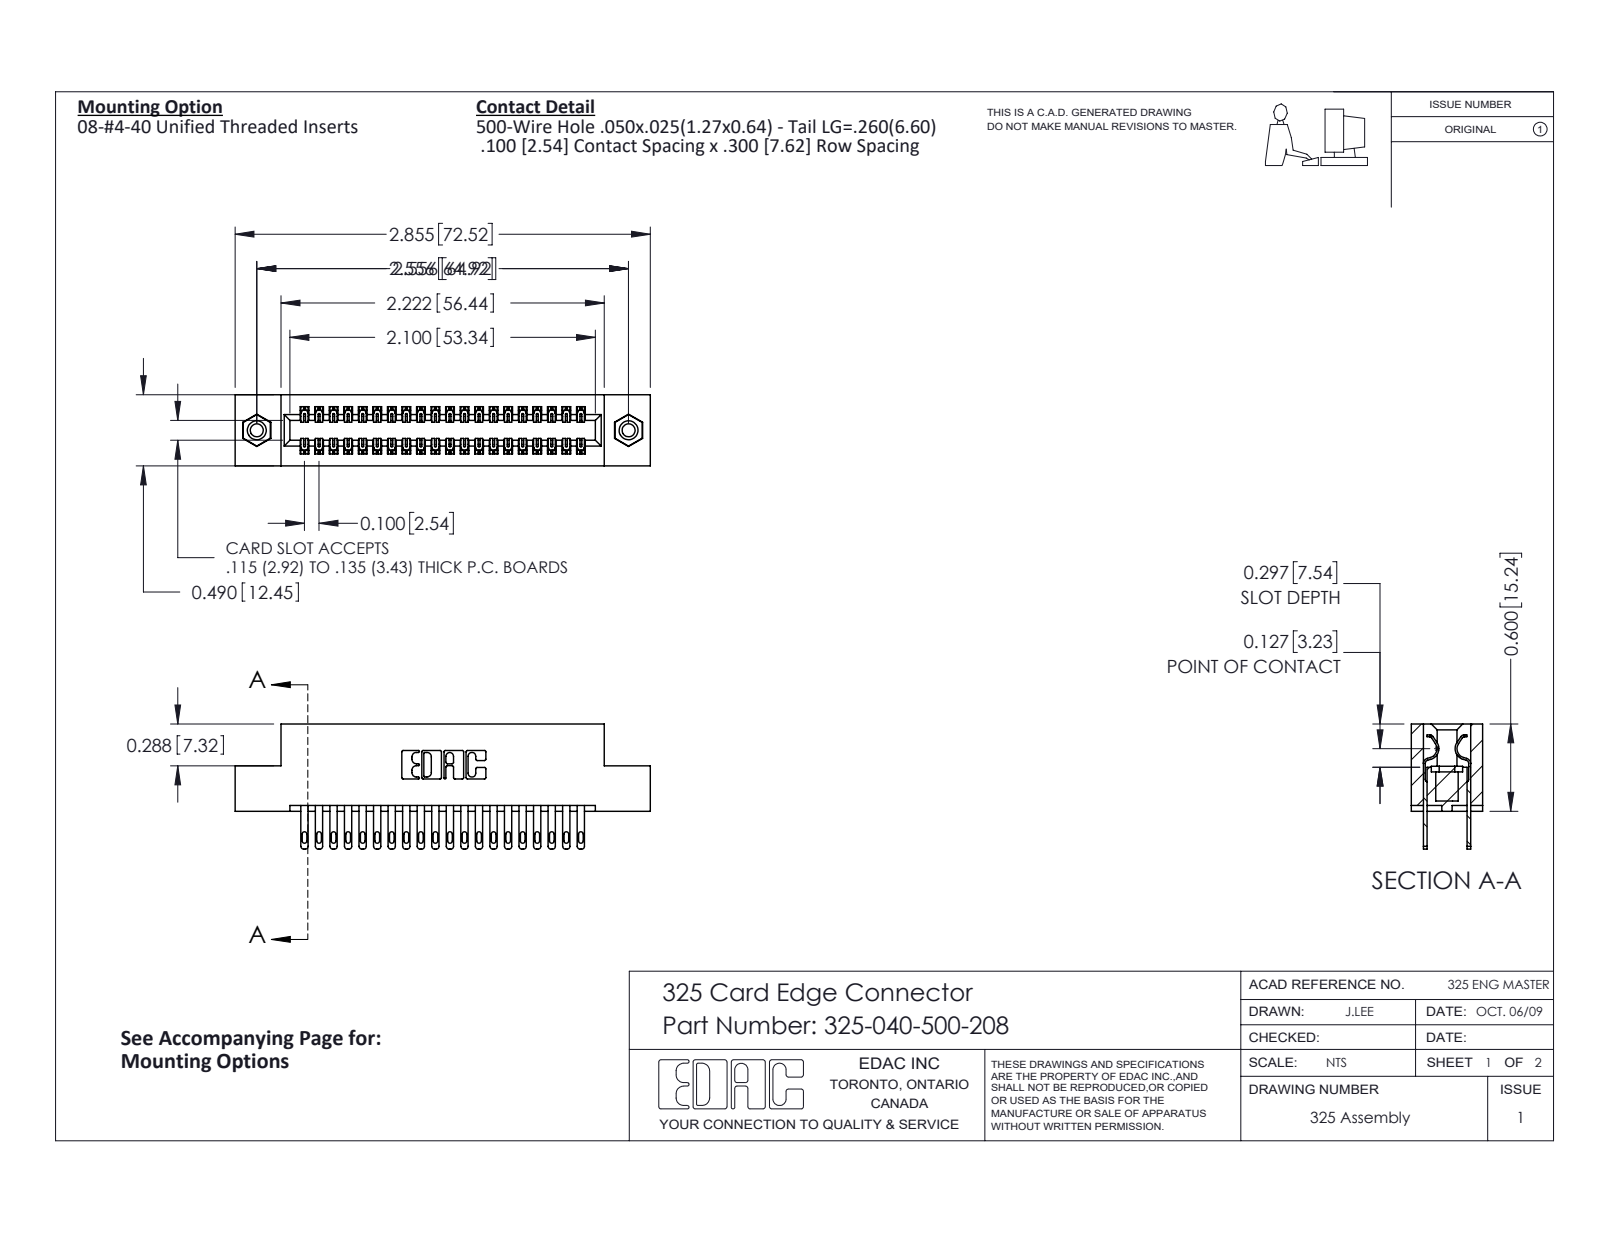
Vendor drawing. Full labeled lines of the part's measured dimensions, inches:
Part name (STEP PRODUCT): 345-250-001_345-250-003-102; 325 Part_TI; 325-292-001_325-293-100; 325-040-500-208
STEP written by: SolidWorks 2016 (CONFIG_CONTROL_DESIGN)
Units: inches
Bodies: 43 solids, 2094 faces (1302 planar, 776 cylindrical, 16 other)
Overall size (bounding box): 2.855 × 0.86 × 0.49
Volume: 0.566 in³ · Surface area: 17.27 in²
Round holes (diameter × count): ⌀0.089 ×2, ⌀0.125 ×2, ⌀0.16 ×2
Round bosses / shafts (diameter × count): ⌀0.155 ×2
Partial cylindrical surfaces — rounded edges, fillets, slot ends (radius × count): R0.006 ×60, R0.016 ×40, R0.02 ×40, R0.01 ×22, R0.007 ×6, R0.031 ×6, R0.026 ×3, R0.014 ×2
Main face-to-face distances: 0.083, 0.407, 0.3, 0.107, 0.383, 0.025, 0.49, 0.325, 0.04, 0.275
Hole centre spacings: 2.556
